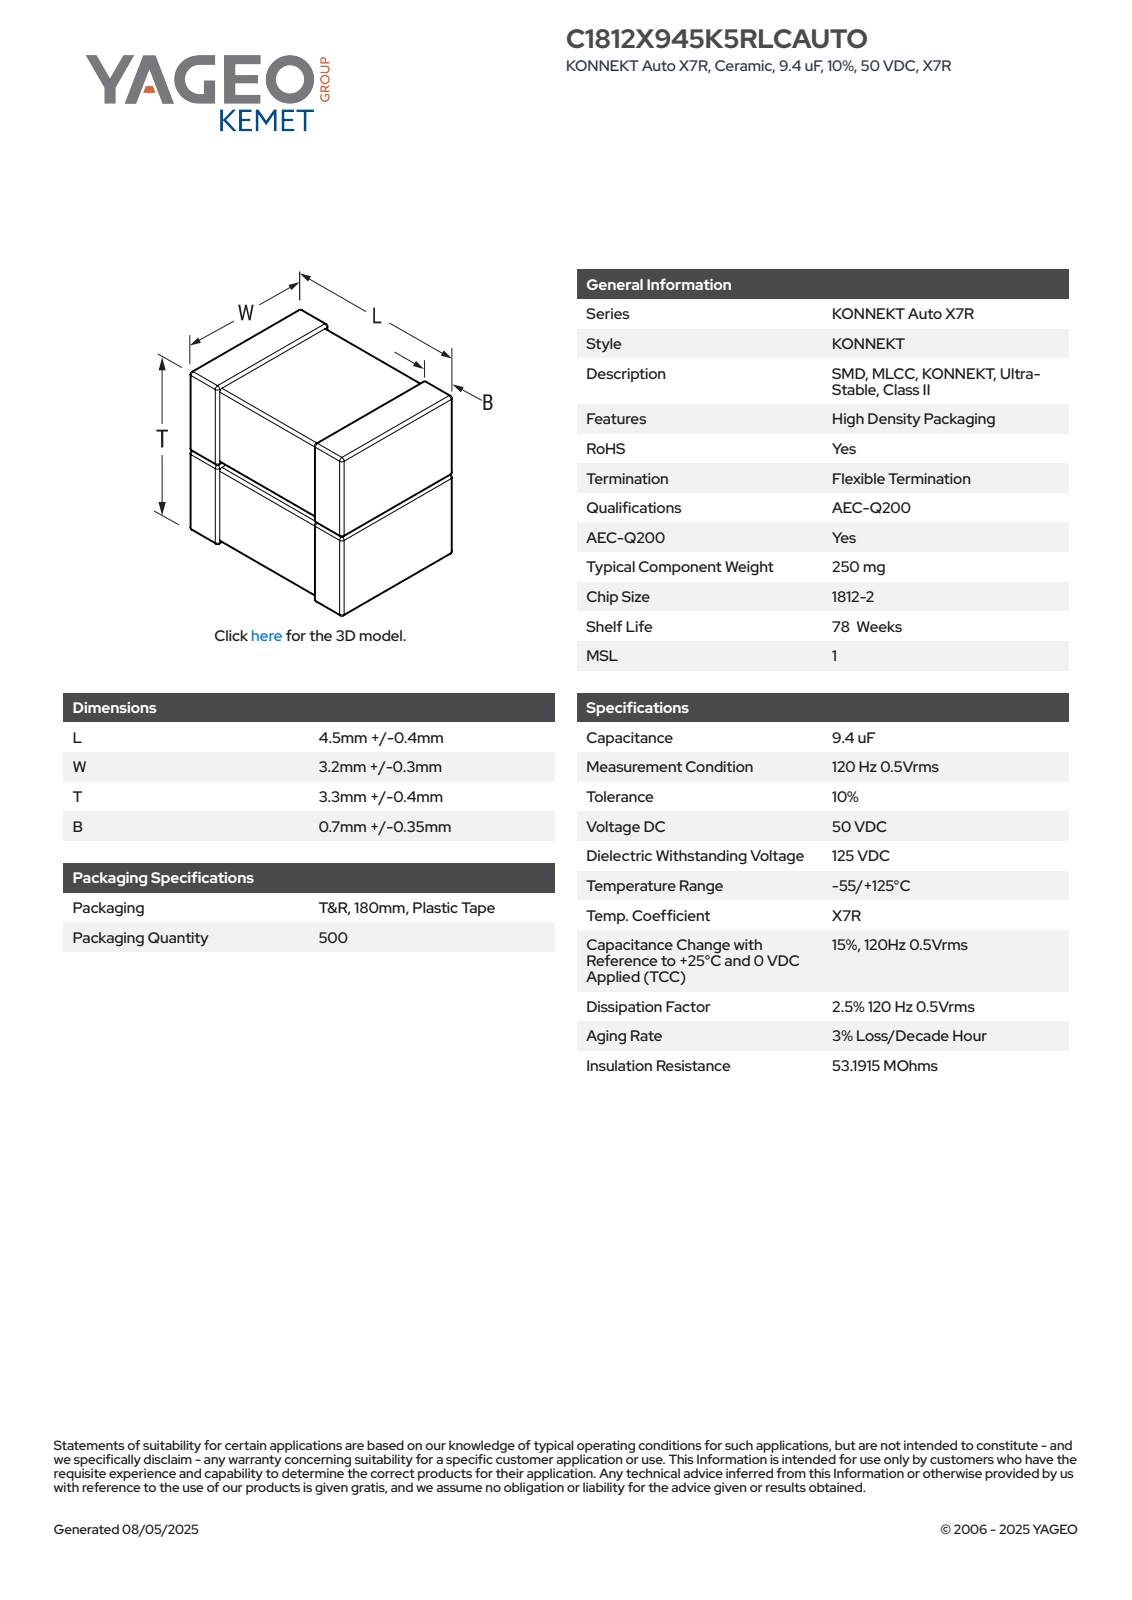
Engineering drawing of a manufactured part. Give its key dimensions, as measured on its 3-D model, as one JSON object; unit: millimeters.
{"part_name": "CCSS_K2T_1812-2_L4.9W3.5B1.05T3.7", "step_written_by": "SolidWorks 2020 (AUTOMOTIVE_DESIGN)", "units": "millimeters", "bodies": {"solids": 4, "faces": 189, "planar": 81, "cylindrical": 76, "other": 32}, "overall_size": [4.9, 3.7, 3.5], "volume_mm3": 59, "surface_area_mm2": 116, "face_to_face_distances": [1.85, 1.71, 3.43, 1.78, 1.92, 3.63, 4.9, 3.56, 3.36, 3.5]}
